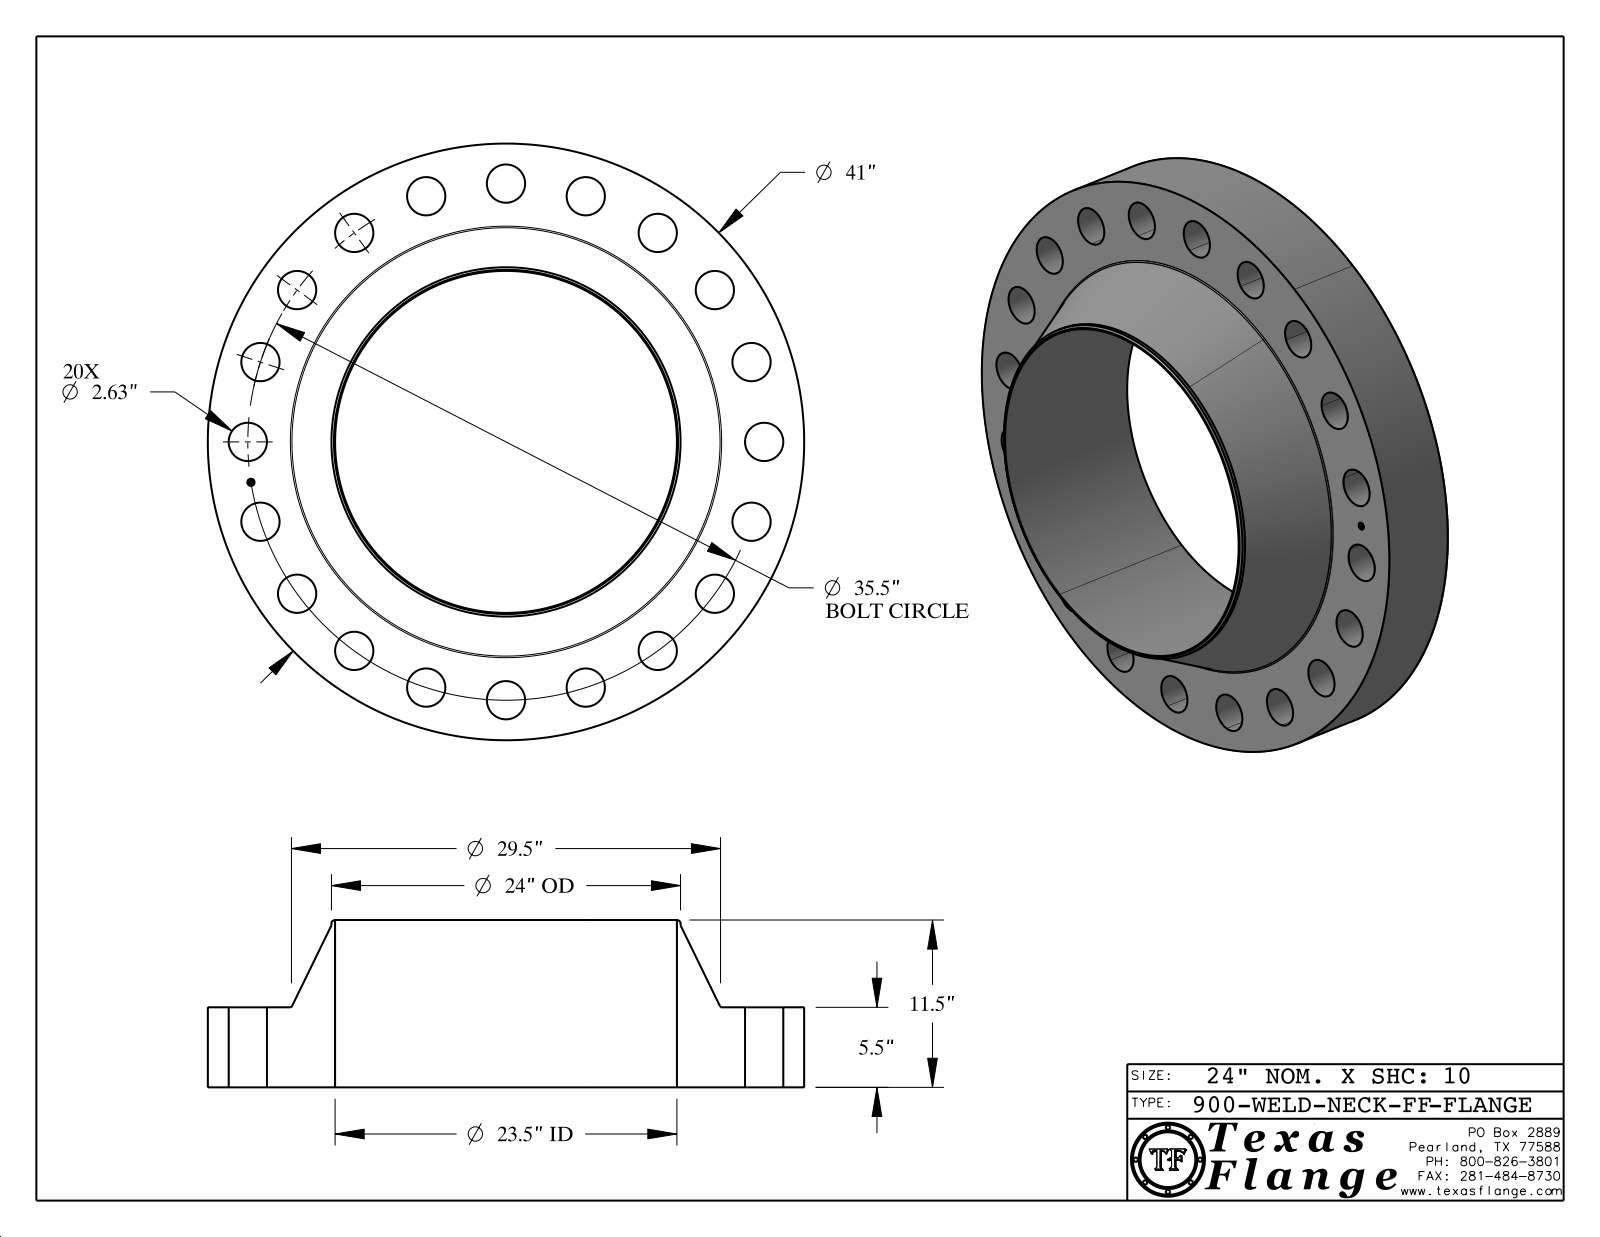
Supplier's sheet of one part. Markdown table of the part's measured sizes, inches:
| quantity | value |
| --- | --- |
| part name | 900-WELD-NECK-FF |
| STEP written by | CATIA V5 STEP AP214 (AUTOMOTIVE_DESIGN) |
| units | inches |
| bodies | 1 solid, 440 faces (368 planar, 66 cylindrical, 6 other) |
| overall size | 41 × 41 × 11.5 |
| volume | 5 018 in³ |
| surface area | 4 337 in² |
| round holes (diameter × count) | 2.63 × 20, 0.495 × 1, 23.5 × 1 |
| round bosses / shafts (diameter × count) | 0.03 × 8, 41 × 1, 24 × 1, 0.39 × 1 |
| main face-to-face distances | 5.5, 11.5, 6, 5.485, 0.015, 6.015, 0.148, 0.144, 0.027, 0.096 |
| hole center spacings | 17.75, 10.97, 28.72, 31.631, 16.117, 20.866, 25.102, 33.762 |
